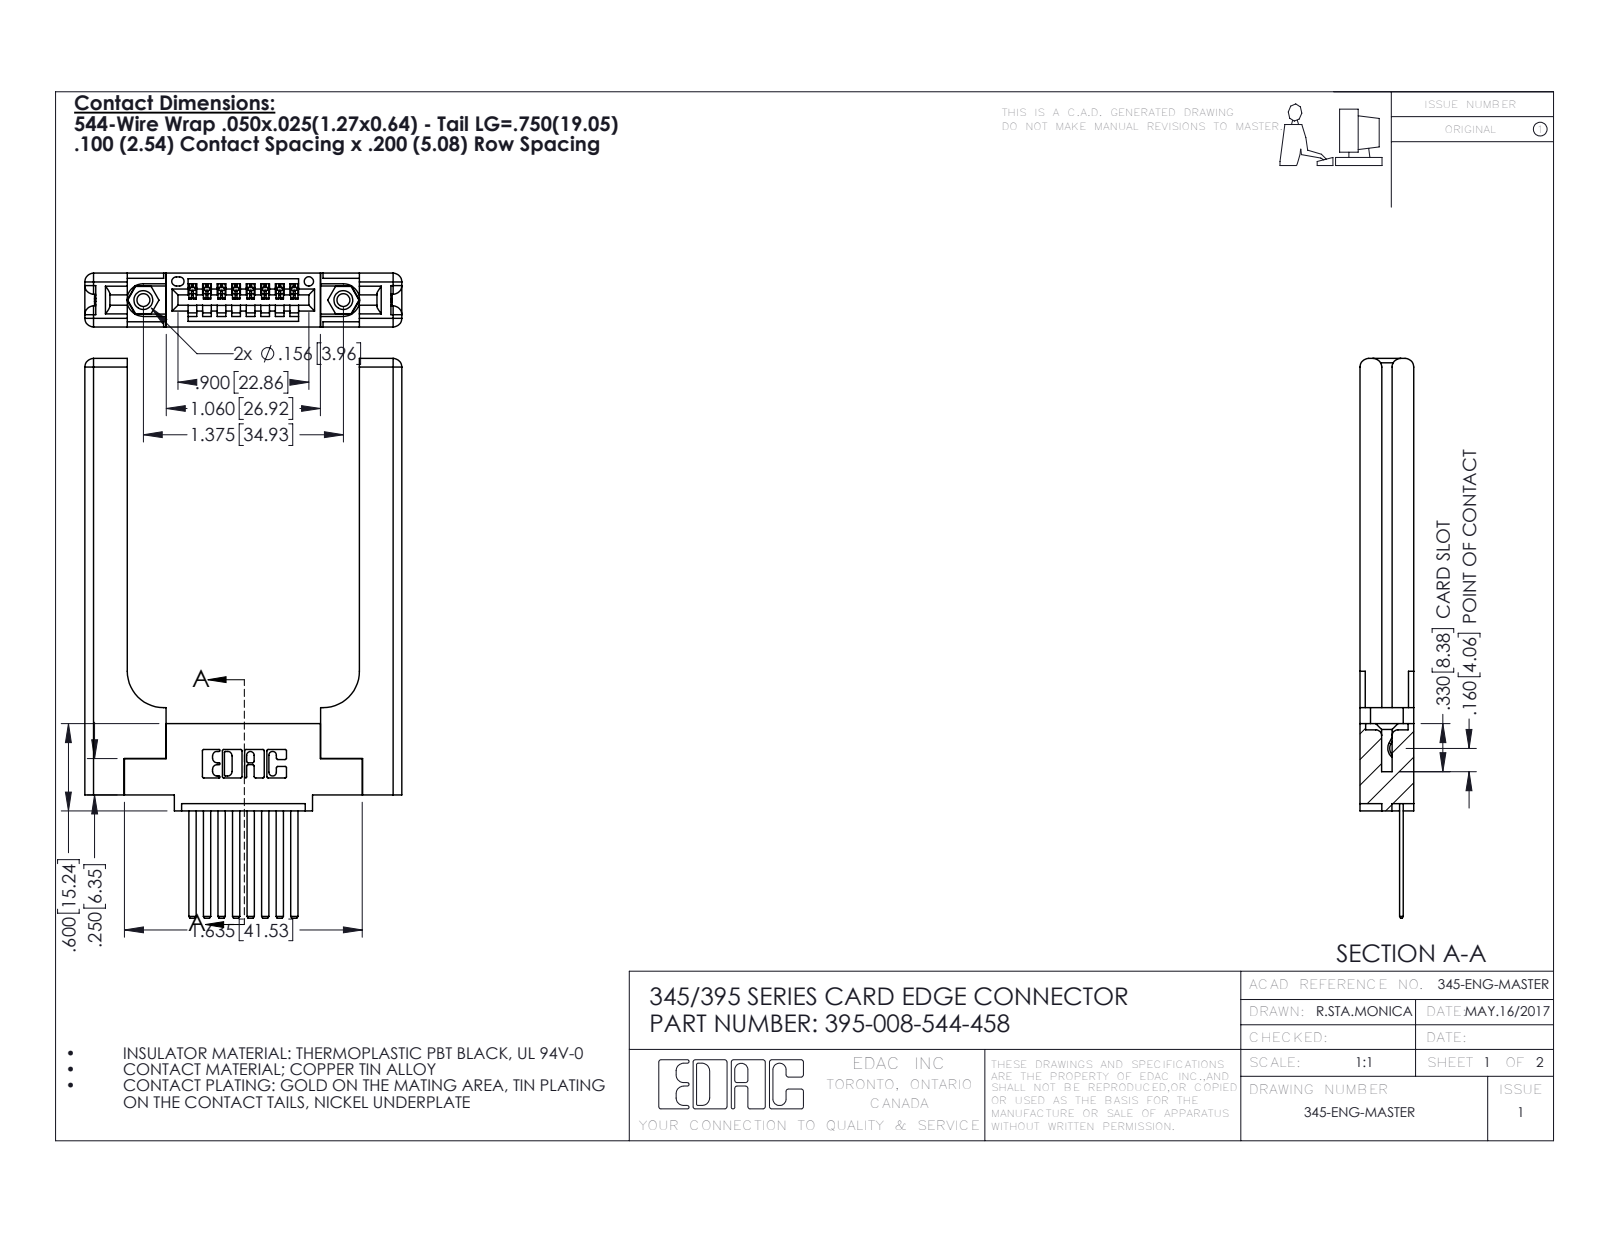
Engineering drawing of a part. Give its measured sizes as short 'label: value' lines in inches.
name: 395-008-544-458; 345-292-001_345-293-144; 345 Part_0.110 Offset - 0.156 Dia-TH; 345-250-001_345-250-001-102 (+1 more)
written by: SolidWorks 2016 (CONFIG_CONTROL_DESIGN)
unit: in
bodies: 13 solids, 802 faces (520 planar, 222 cylindrical, 60 other)
size: 3.847 × 2.179 × 0.37
volume: 0.824 in³; area: 18.36 in²
holes: 2× ⌀0.089, 2× ⌀0.125, 2× ⌀0.156, 1× ⌀0.064
bosses: 2× ⌀0.155
rounds: 22× R0.01, 16× R0.006, 16× R0.06, 6× R0.007, 6× R0.031, 3× R0.026, 2× R0.03, 2× R0.031
face distances: 0.37, 0.072, 0.15, 0.22, 0.298, 0.148, 0.077, 1.596, 0.098, 0.272
hole spacings: 0.27, 1.144, 1.375
